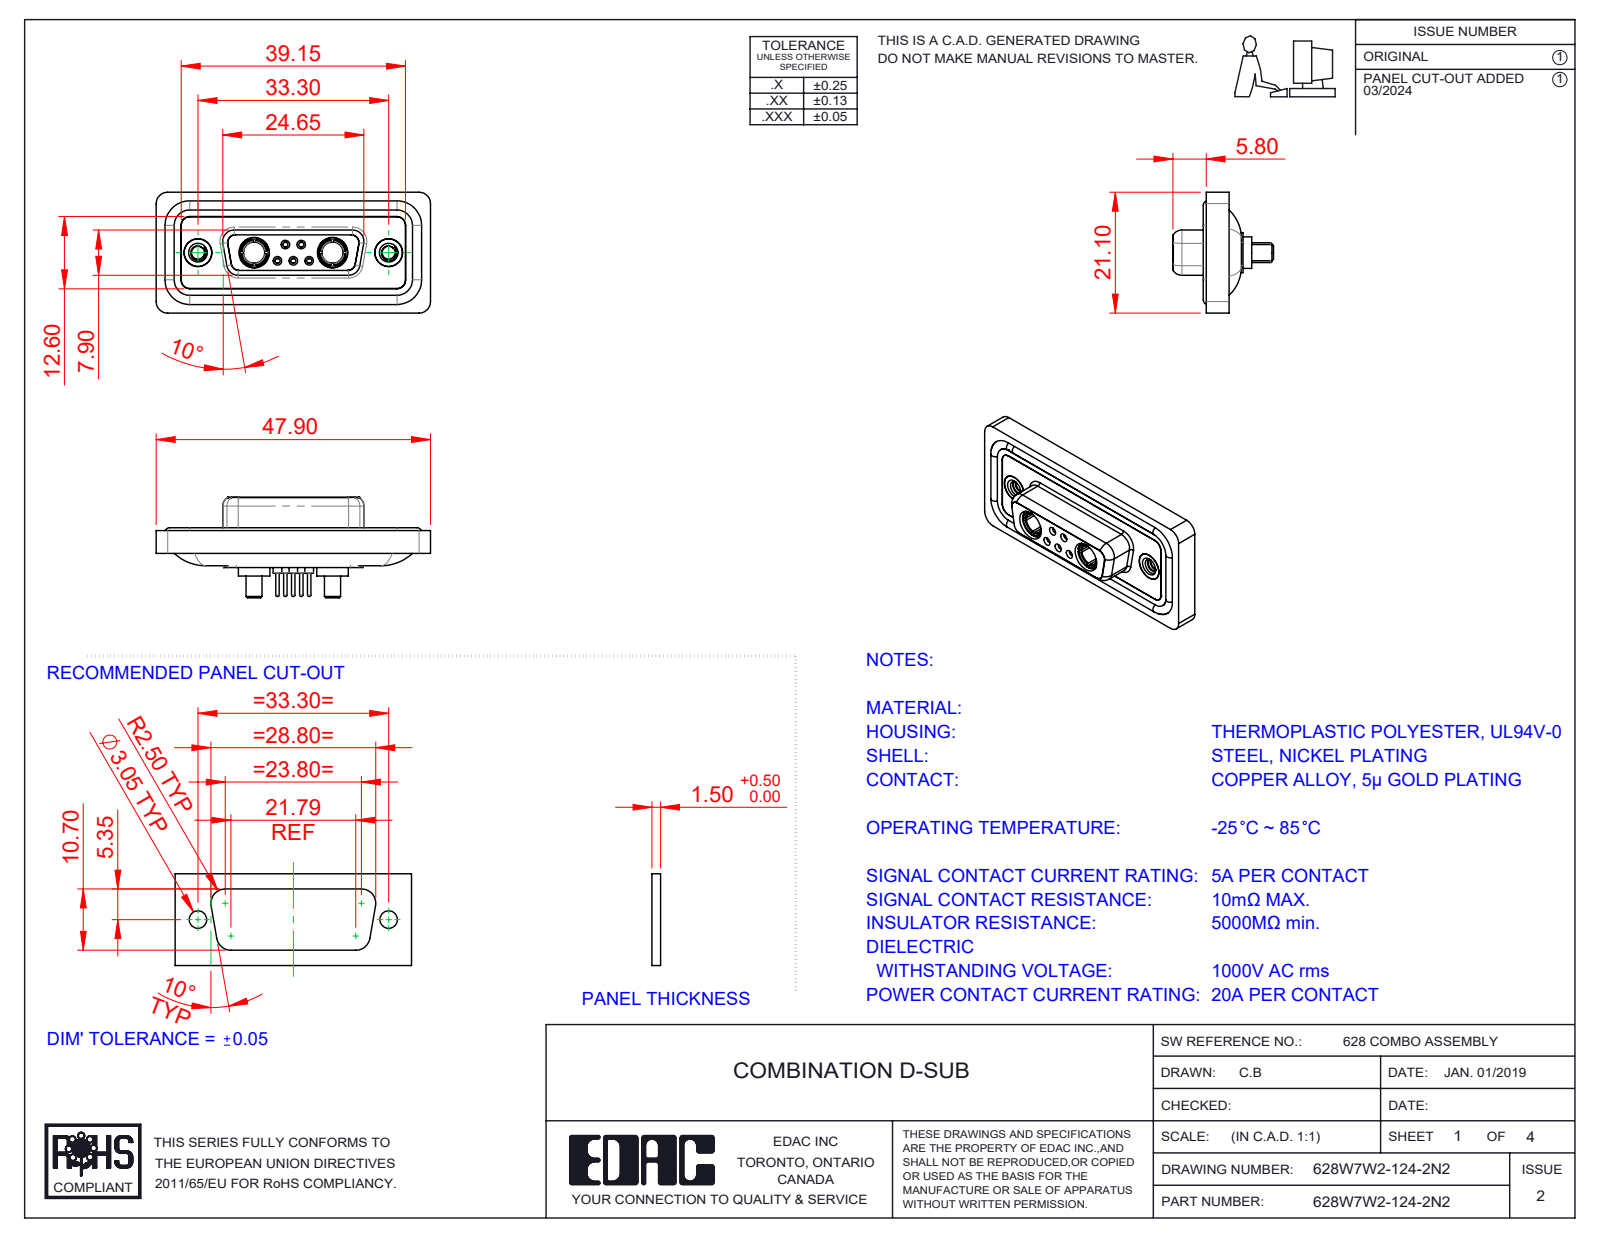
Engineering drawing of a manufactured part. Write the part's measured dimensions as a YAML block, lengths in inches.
part_name: "628W7W2-124-2N2; Power Socket_20A S; 628Combo Waterproof Housing_15 Contacts; 628Combo Contact Row 2_24 (+5 more)"
step_written_by: "SolidWorks 2023 (CONFIG_CONTROL_DESIGN)"
units: inches
bodies: {solids: 16, faces: 809, planar: 238, cylindrical: 329, other: 242}
overall_size: [1.886, 0.831, 0.691]
volume: 0.371
surface_area: 15.32
round_holes:
  - {diameter: 0.035, count: 5}
  - {diameter: 0.043, count: 5}
  - {diameter: 0.059, count: 5}
  - {diameter: 0.079, count: 5}
  - {diameter: 0.191, count: 4}
  - {diameter: 0.063, count: 3}
  - {diameter: 0.067, count: 2}
  - {diameter: 0.089, count: 2}
  - {diameter: 0.146, count: 2}
  - {diameter: 0.157, count: 2}
  - {diameter: 0.159, count: 2}
  - {diameter: 0.197, count: 2}
round_bosses_or_shafts:
  - {diameter: 0.063, count: 6}
  - {diameter: 0.087, count: 5}
  - {diameter: 0.024, count: 5}
  - {diameter: 0.217, count: 2}
  - {diameter: 0.205, count: 2}
  - {diameter: 0.195, count: 2}
  - {diameter: 0.195, count: 2}
  - {diameter: 0.189, count: 2}
partial_cylinders:
  - {radius: 0.059, count: 22}
  - {radius: 0.079, count: 20}
  - {radius: 0.053, count: 12}
  - {radius: 0.063, count: 8}
  - {radius: 0.01, count: 4}
  - {radius: 0.02, count: 4}
  - {radius: 0.024, count: 4}
  - {radius: 0.026, count: 4}
face_to_face_distances: [0.016, 0.071, 0.063, 0.02, 0.114, 0.293, 0.043, 0.222, 0.26, 0.278]
hole_center_spacings: [0.124, 0.109, 0.386, 0.925, 0.17, 0.17, 0.198, 0.198]
